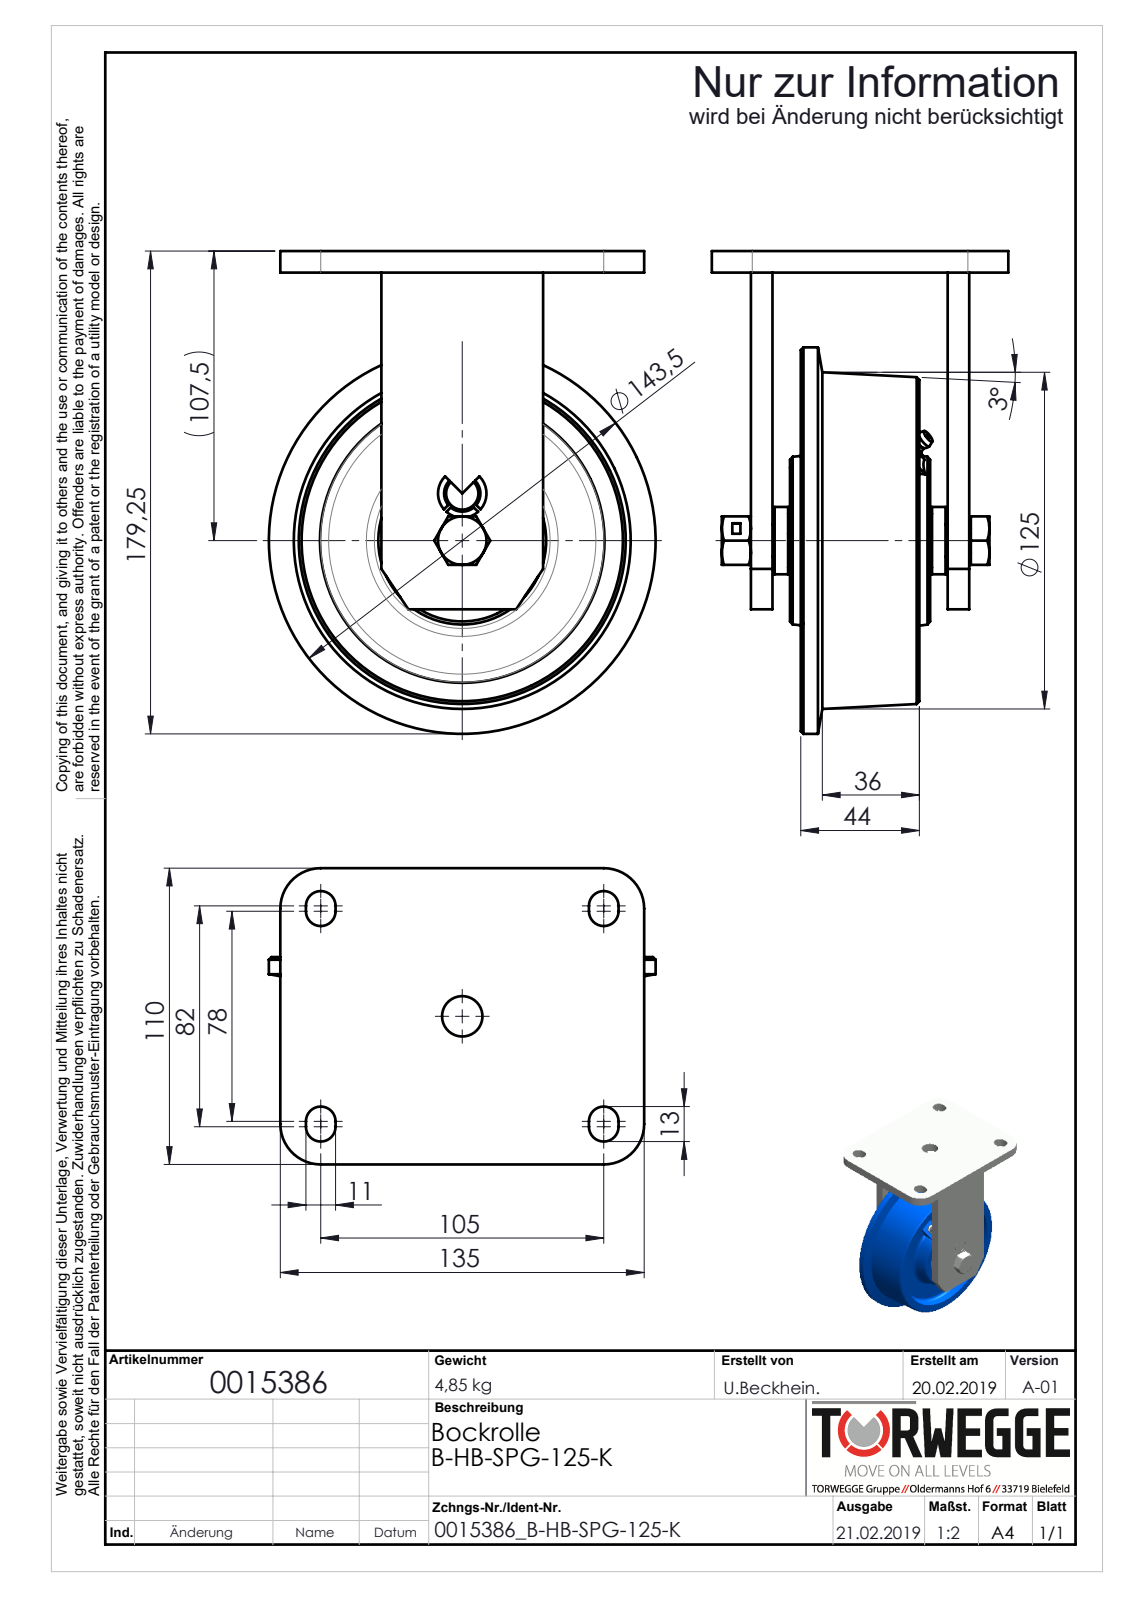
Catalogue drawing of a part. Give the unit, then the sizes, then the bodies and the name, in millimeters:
Units: millimetres
Overall size (bounding box): 179.25 × 143.5 × 110
Round holes (diameter × count): ⌀5.7 ×1, ⌀10.2 ×1, ⌀12 ×1, ⌀12.2 ×1, ⌀12.5 ×1, ⌀15 ×1, ⌀20 ×1, ⌀20.4 ×1, ⌀28.1 ×1, ⌀35 ×1, ⌀38.9 ×1, ⌀47 ×1
Round bosses / shafts (diameter × count): ⌀143.5 ×1, ⌀25 ×1, ⌀18 ×1, ⌀6 ×1
Partial cylindrical surfaces — rounded edges, fillets, slot ends (radius × count): R5.5 ×8, R15 ×4, R6 ×1, R6.75 ×1, R9 ×1, R16.07 ×1, R17.43 ×1
Main face-to-face distances: 8, 73, 18.5, 62.5, 10.5, 54.5, 81, 65, 16.5, 53.38
Volume: 654 121 mm³ · Surface area: 174 463 mm²
Bodies: 20 solids, 366 faces (140 planar, 111 cylindrical, 115 other)
Part name (STEP PRODUCT): 0015386_B-HB-SPG-125-K_(A-01)
STEP written by: SolidWorks 2018 (AUTOMOTIVE_DESIGN)
